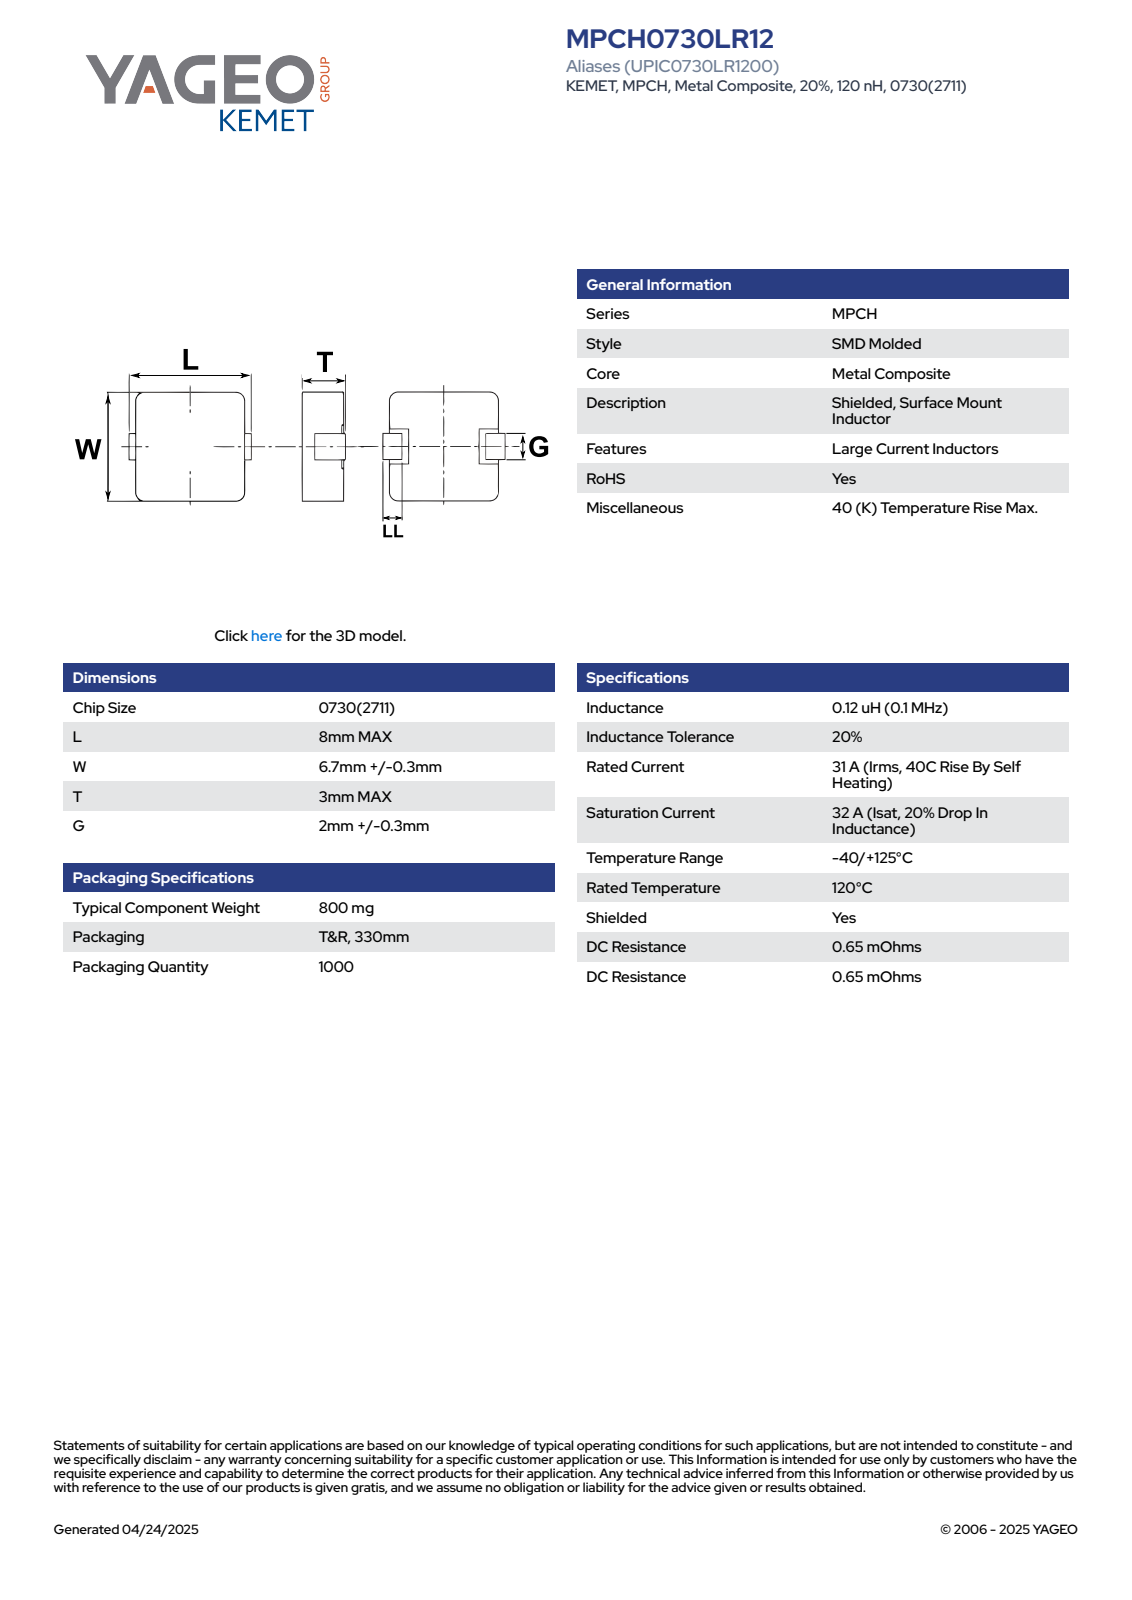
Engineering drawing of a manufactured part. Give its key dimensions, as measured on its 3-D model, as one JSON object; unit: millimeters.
{"part_name": "IS_MPC_3126_L8W7T3LL1.5G2.3", "step_written_by": "SolidWorks 2014 (AUTOMOTIVE_DESIGN)", "units": "millimeters", "bodies": {"solids": 4, "faces": 105, "planar": 93, "cylindrical": 12, "other": 0}, "overall_size": [8, 7, 3], "volume_mm3": 157, "surface_area_mm2": 216, "partial_cylinders_radius": [[0.6, 4]], "face_to_face_distances": [2.95, 7, 7.59, 7.8, 7.58, 7.6, 7.79, 7.9, 7.69, 7.7]}
